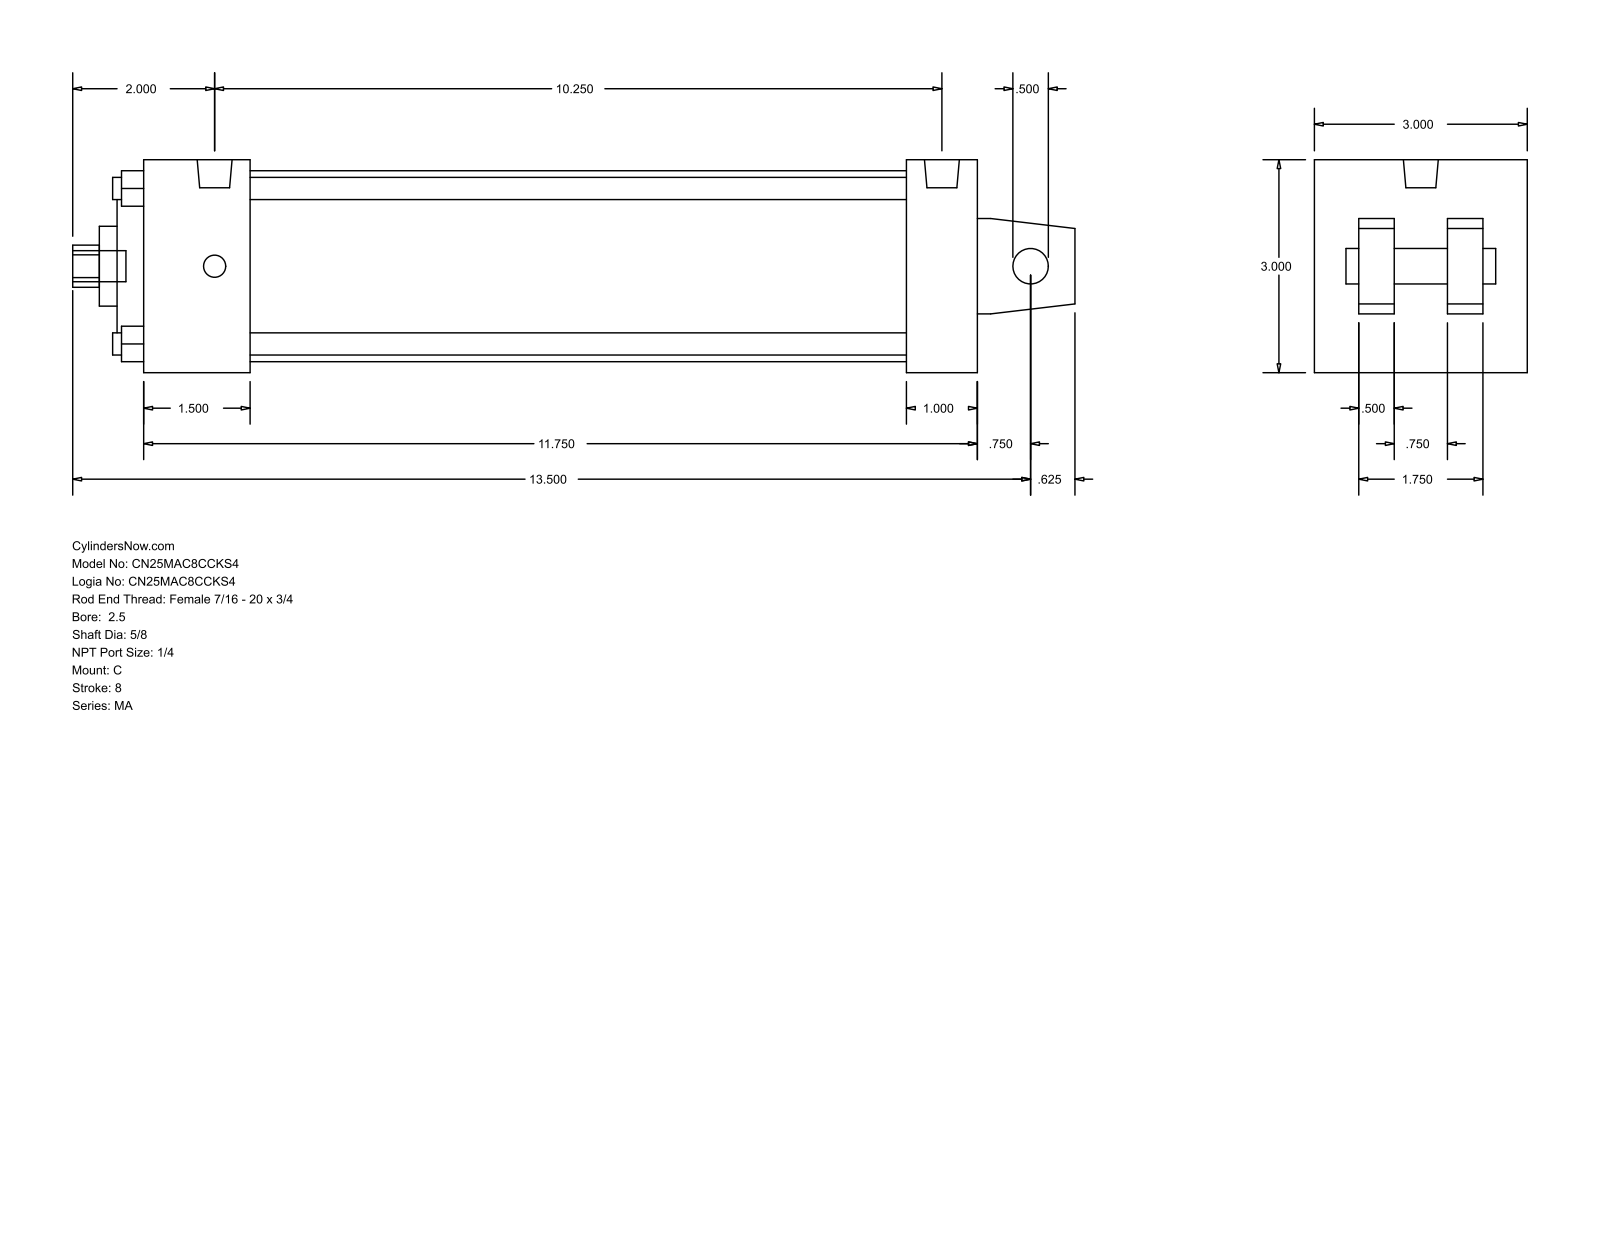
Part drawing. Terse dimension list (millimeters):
name: MA_C__0250_0.625
written by: GSSL Pune (CONFIG_CONTROL_DESIGN)
unit: mm
bodies: 0 solids, 105 faces (77 planar, 28 cylindrical, 0 other)
size: 358.77 × 76.2 × 76.2
holes: 4× ⌀7.94, 1× ⌀12.7, 1× ⌀15.88, 1× ⌀28.57, 1× ⌀50.8, 1× ⌀68.33
bosses: 4× ⌀7.94, 2× ⌀12.49, 1× ⌀11.11
rounds: 1× R7.54
face distances: 76.2, 298.45, 12.7, 15.87, 47.63, 25.4, 38.1, 273.05, 234.95, 260.35
hole spacings: 39.33, 55.62, 78.66
